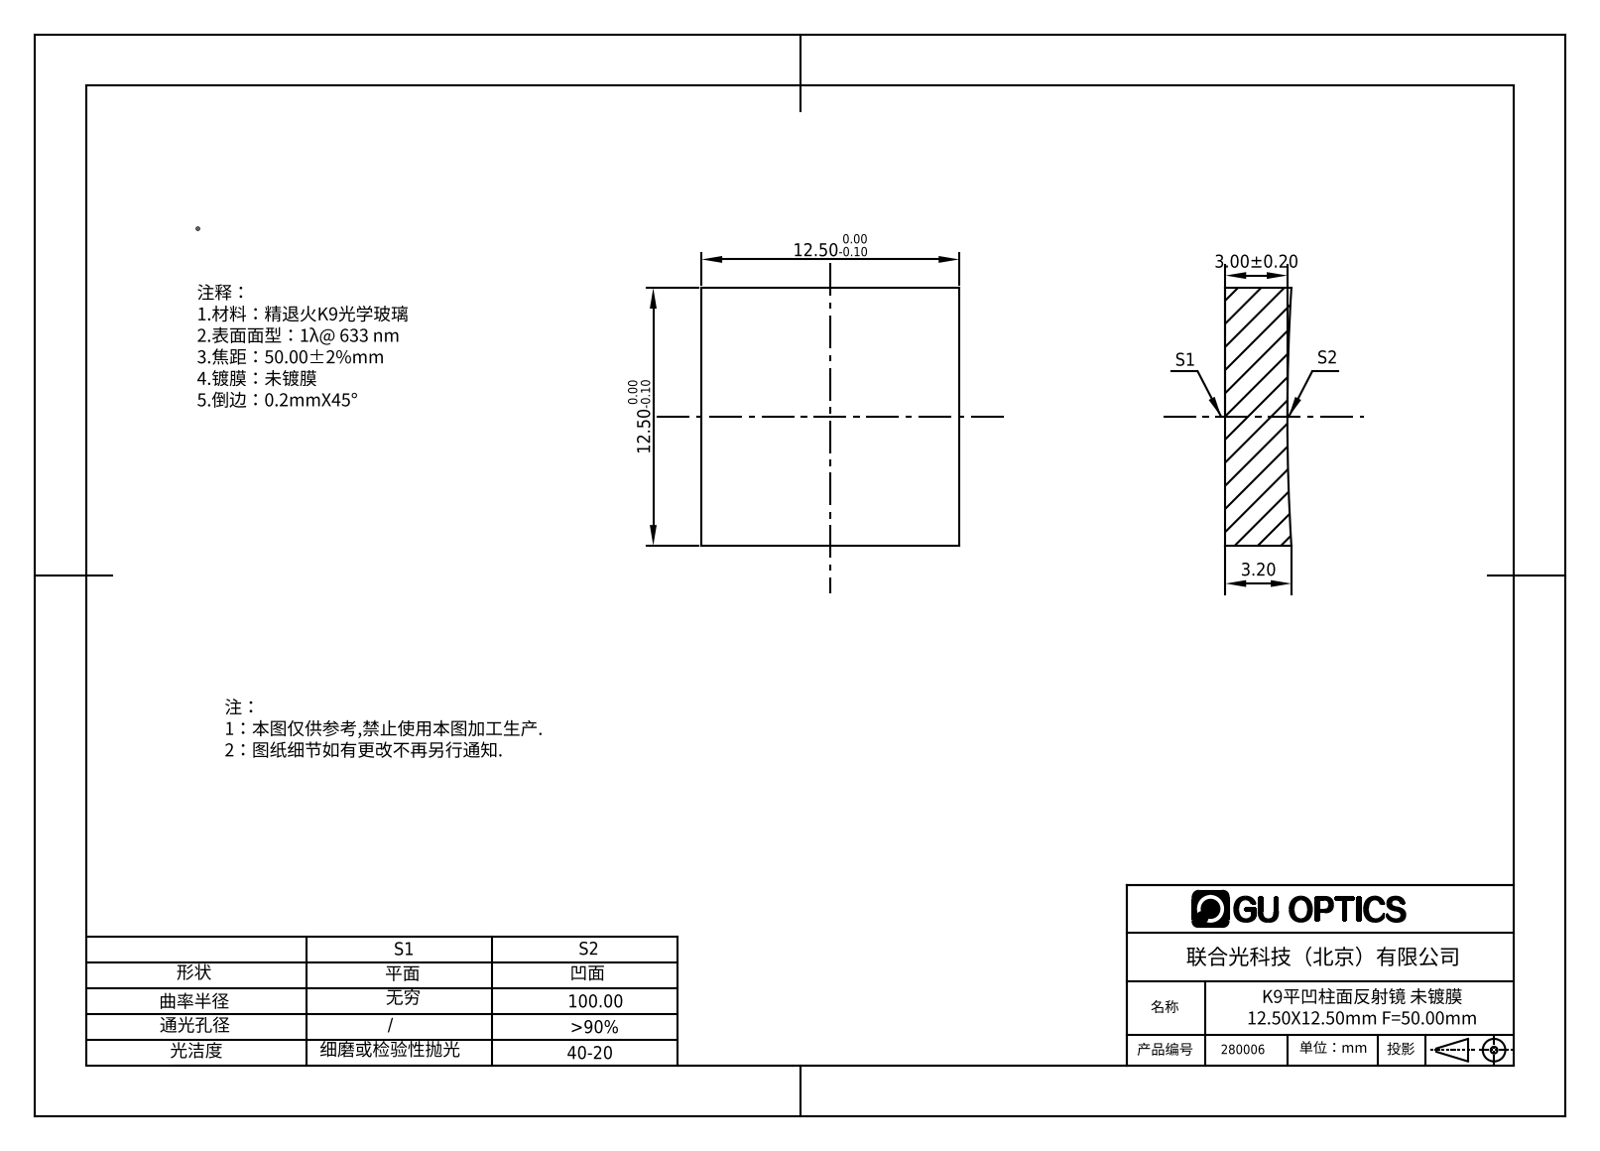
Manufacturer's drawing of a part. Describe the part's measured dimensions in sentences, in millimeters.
The part is named "280006". Its 3-D file was written by "SolidWorks 2016 (AUTOMOTIVE_DESIGN)". It is 1 solid with 7 faces: 5 planar, 2 cylindrical and 0 other. Overall it measures 12.5 by 12.5 by 3.2 millimeters. Its volume is 479 cubic millimeters and its surface area 469 square millimeters. Partial cylindrical surfaces (rounded edges, fillets, slot ends): 1 of radius 100. The main face-to-face distances are 12.5.
